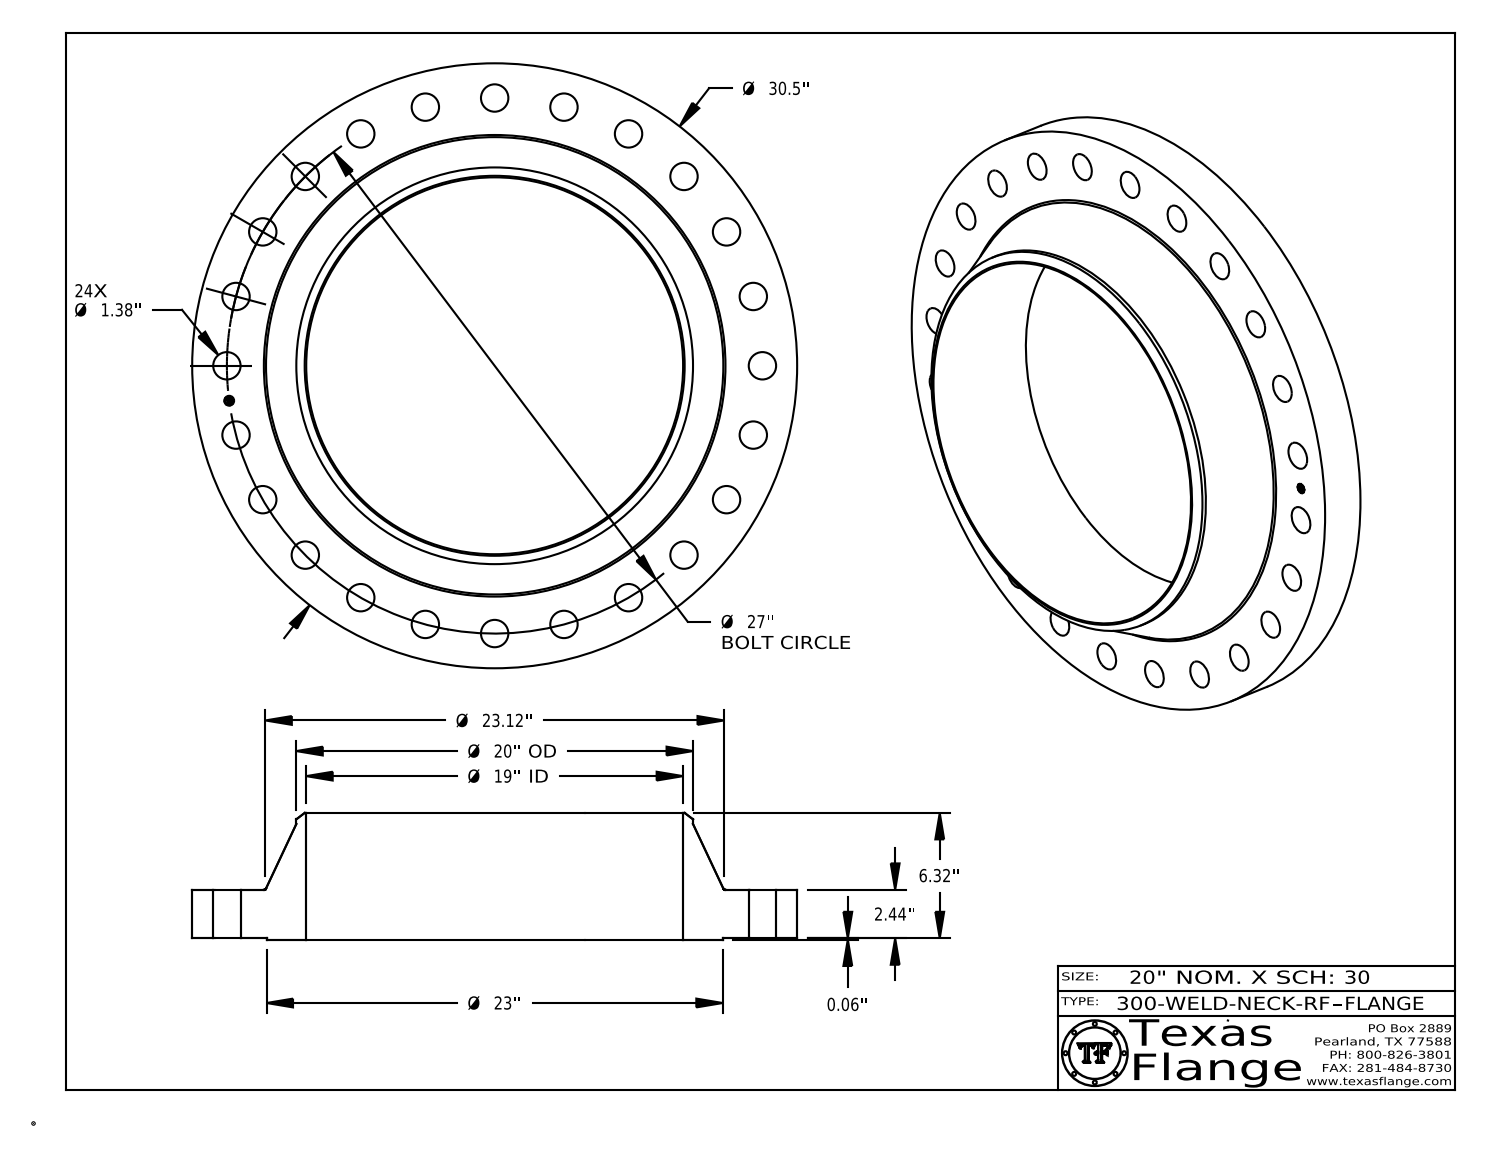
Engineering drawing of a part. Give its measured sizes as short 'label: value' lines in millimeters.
name: 300-WELD-NECK-RF
written by: CATIA V5 STEP AP214 (AUTOMOTIVE_DESIGN)
unit: mm
bodies: 1 solid, 451 faces (369 planar, 76 cylindrical, 6 other)
size: 774.7 × 774.7 × 162.1
volume: 21 250 000 mm³; area: 1 199 000 mm²
holes: 24× ⌀35.1, 1× ⌀12.6, 1× ⌀482.6
bosses: 8× ⌀0.8, 1× ⌀774.7, 1× ⌀584.2, 1× ⌀508, 1× ⌀9.9
face distances: 62, 1.6, 63.6, 162.1, 160.5, 98.6, 63.2, 61.6, 0.4, 98.9
hole spacings: 342.9, 89.5, 177.5, 262.5, 417.5, 633.6, 679.9, 544.1
